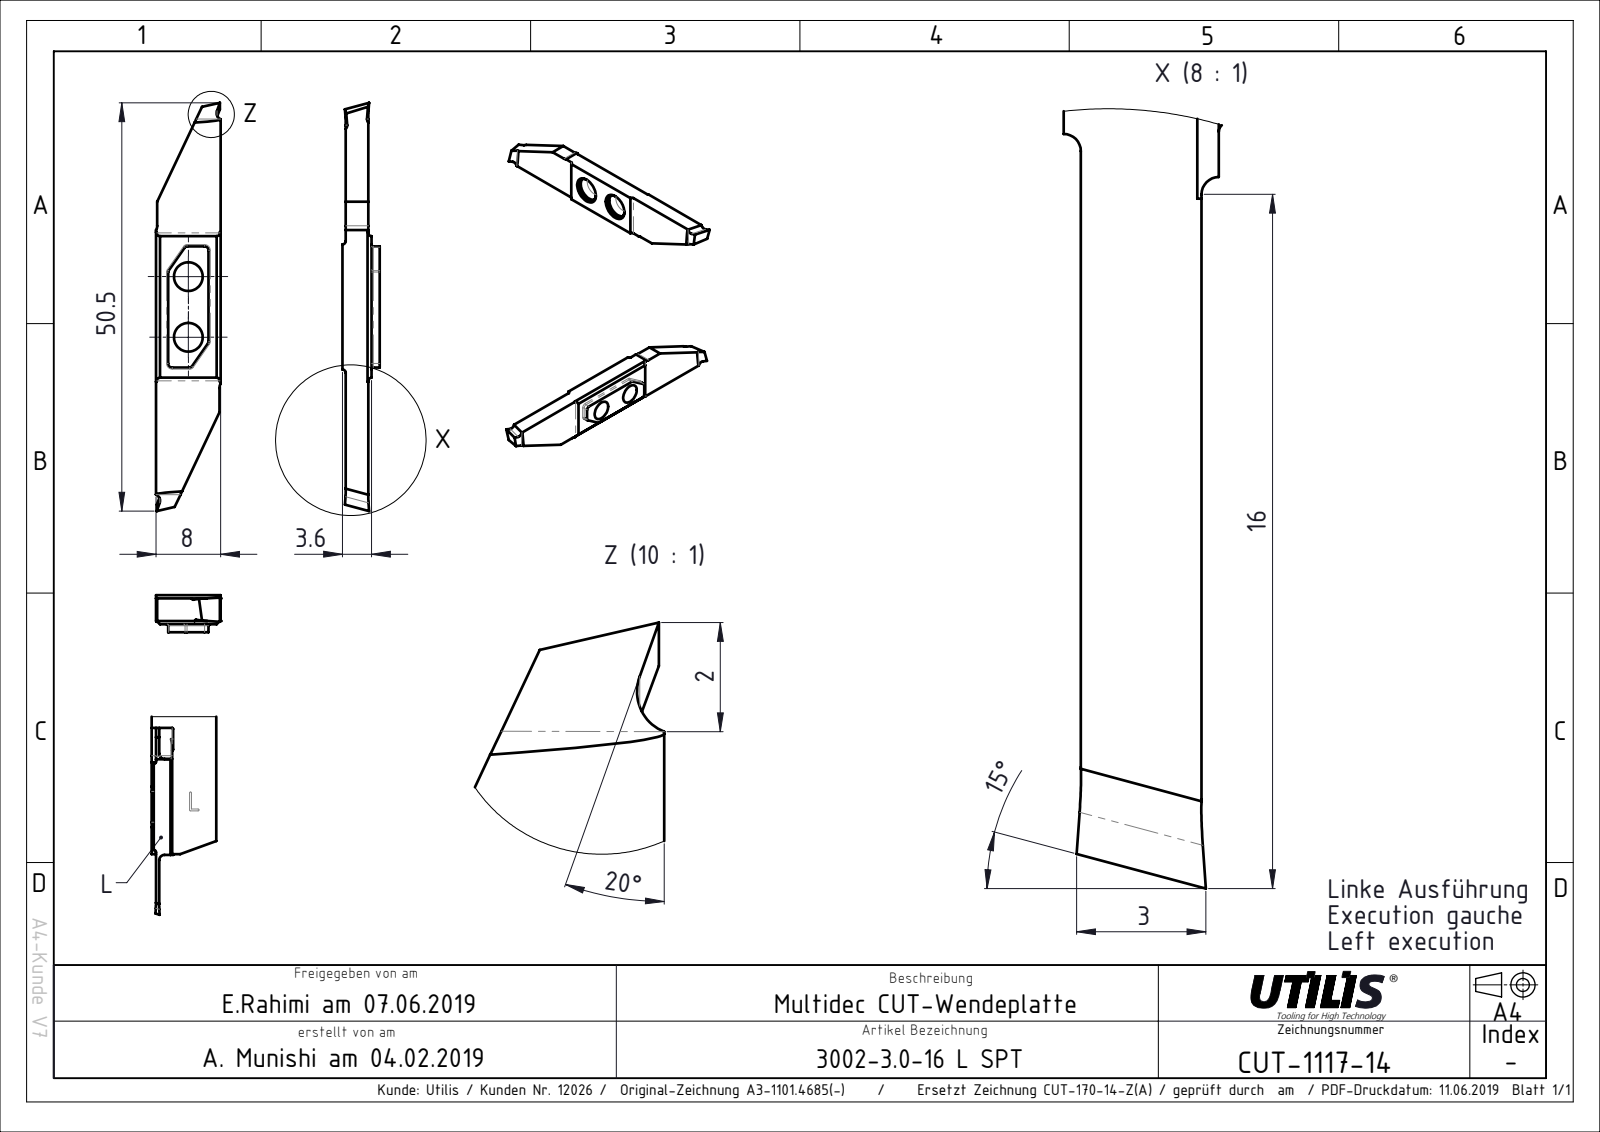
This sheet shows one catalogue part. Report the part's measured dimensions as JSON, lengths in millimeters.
{"part_name": "CUT-1117; ASME Y14.5", "step_written_by": "FormatWorks Professional (AP242_MANAGED_MODEL_BASED_3D_ENGINEERING_MIM_LF)", "units": "millimeters", "bodies": {"solids": 1, "faces": 38, "planar": 28, "cylindrical": 10, "other": 0}, "overall_size": [50.5, 8, 3.6], "volume_mm3": 945, "surface_area_mm2": 1017, "round_holes": [[3.55, 2]], "partial_cylinders_radius": [[0.4, 4], [1, 2]], "face_to_face_distances": [0.41, 3.19, 2.78, 3.6, 8, 18.09, 7.85, 7.7, 1, 16.5], "hole_center_spacings": [7.5]}
